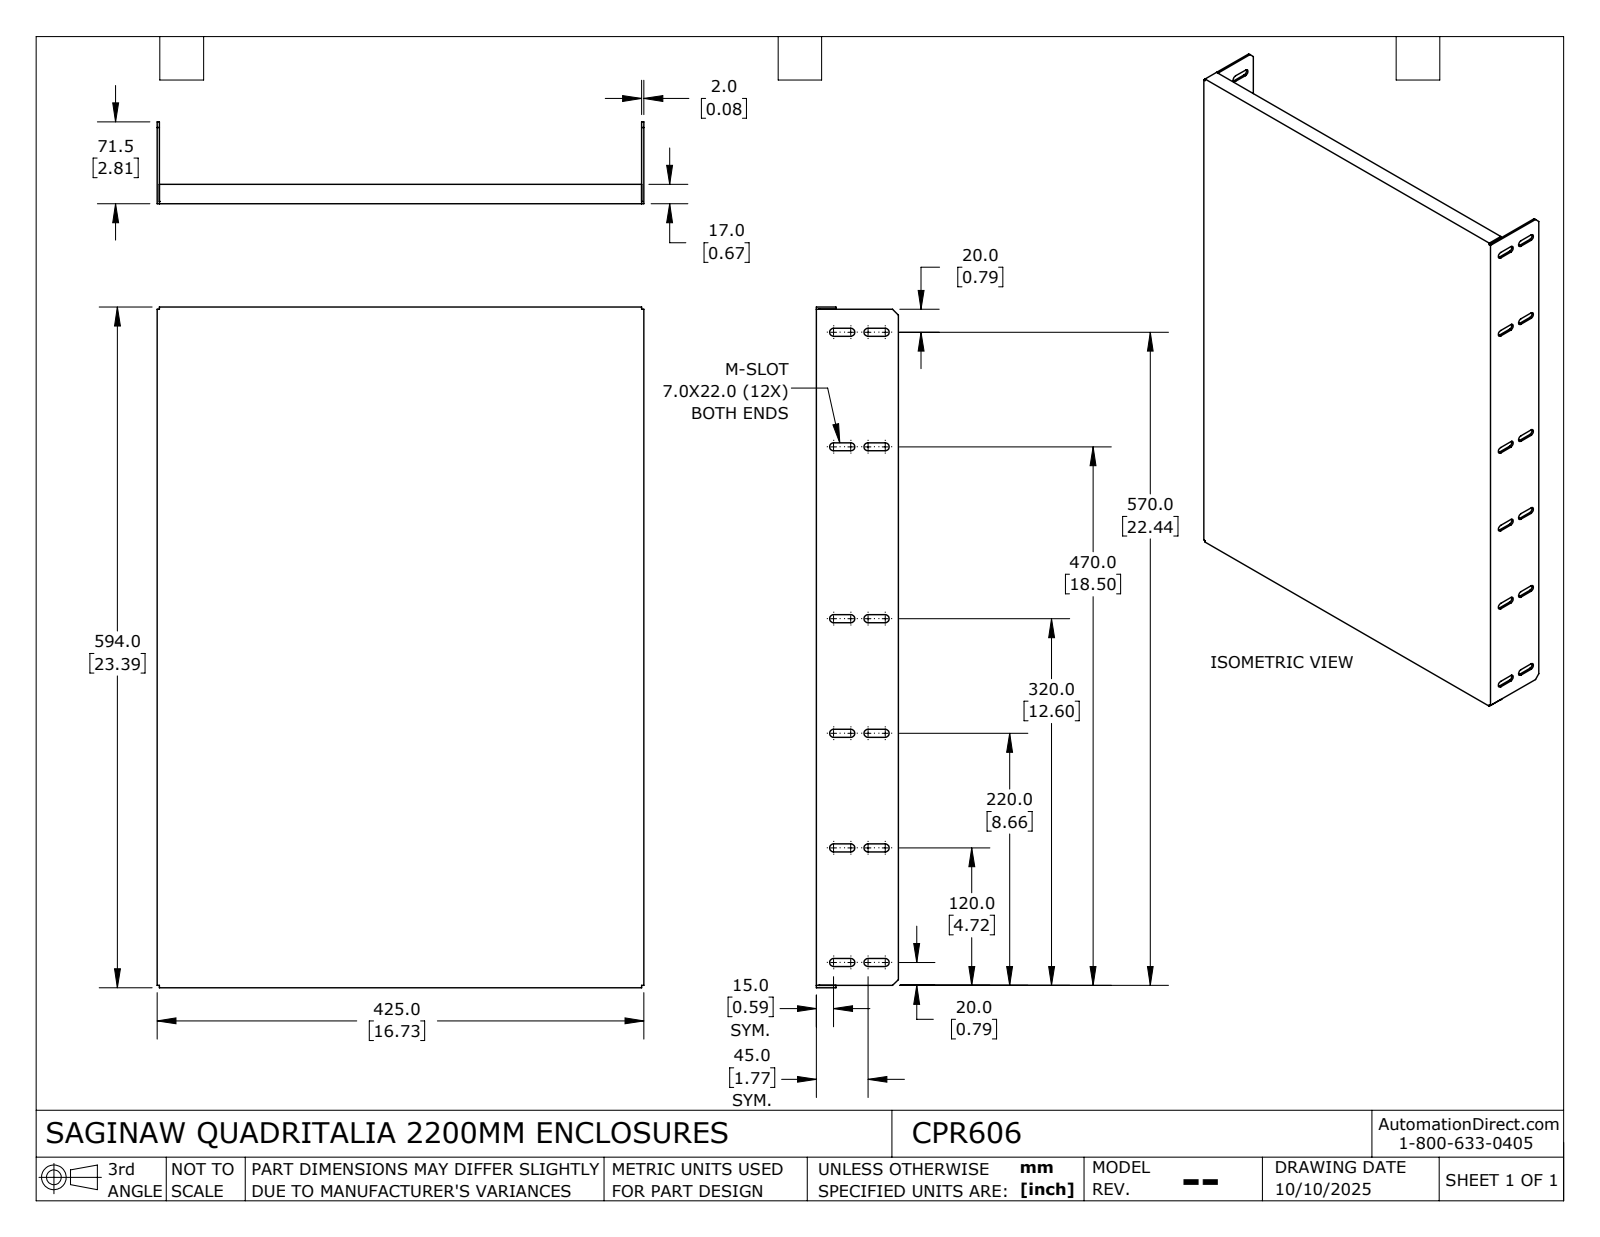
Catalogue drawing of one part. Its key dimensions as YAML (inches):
part_name: "CPR606_Default"
step_written_by: "SolidWorks 2024 (CONFIG_CONTROL_DESIGN)"
units: inches
bodies: {solids: 1, faces: 123, planar: 75, cylindrical: 48, other: 0}
overall_size: [23.386, 16.732, 2.815]
volume: 41.93
surface_area: 1076
partial_cylinders:
  - {radius: 0.138, count: 24}
face_to_face_distances: [0.079, 16.654, 16.732, 16.575, 23.307, 23.386, 23.228, 2.815, 2.736, 0.669]
